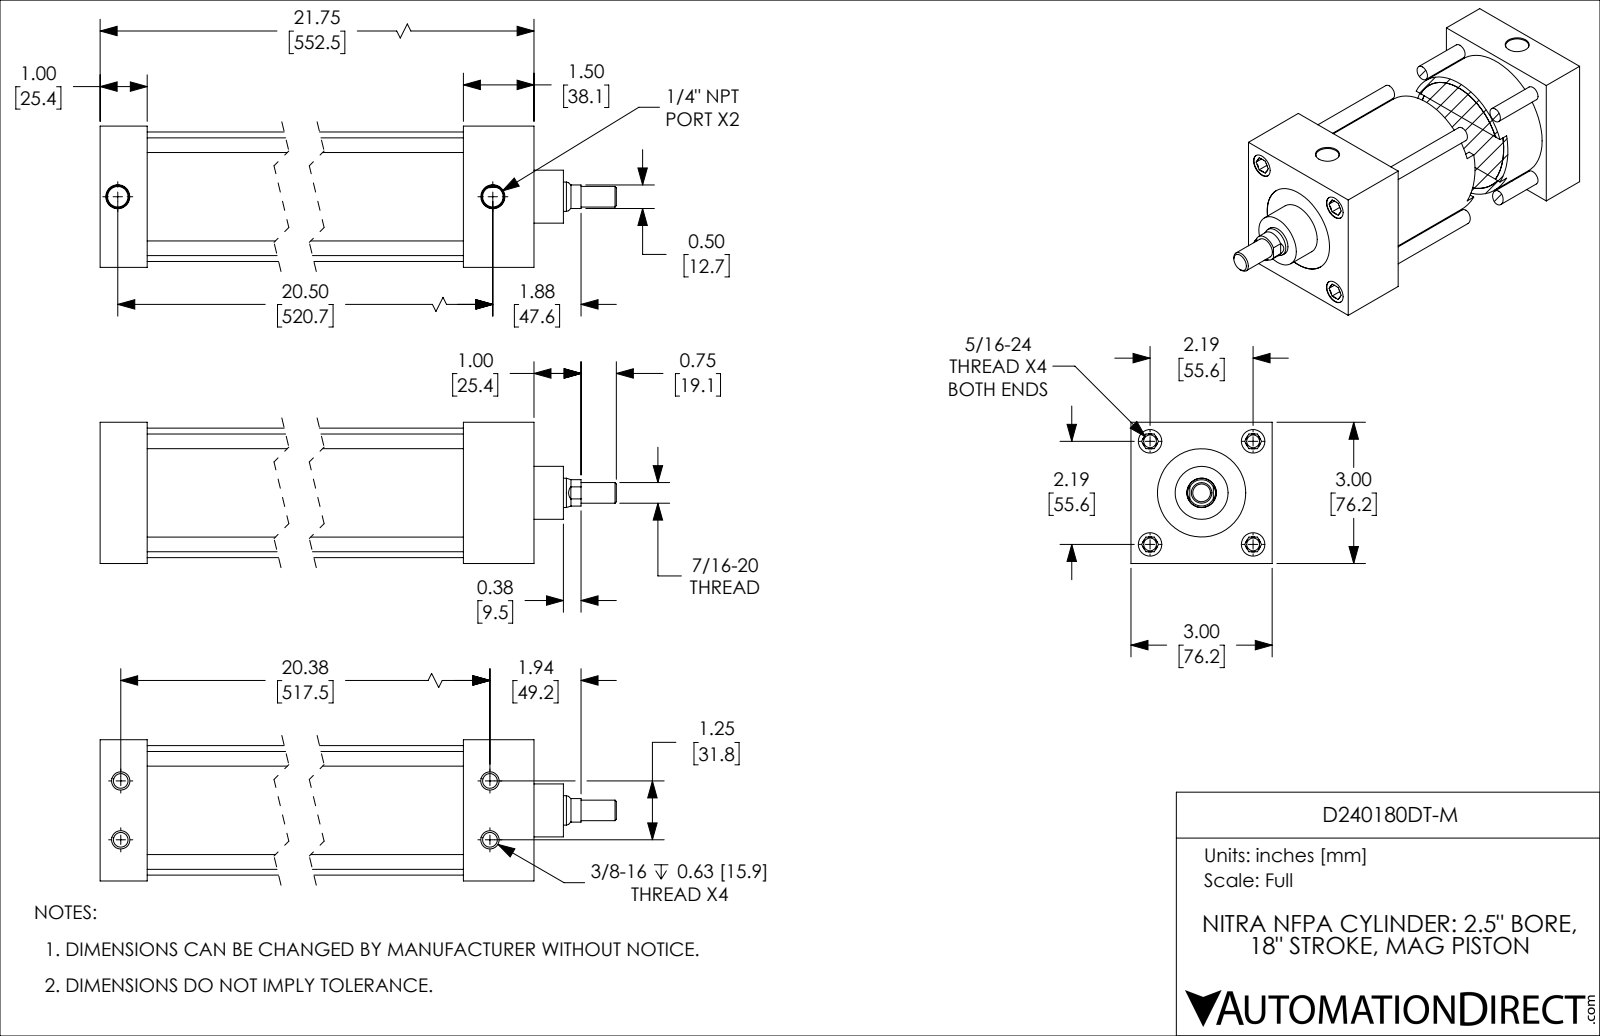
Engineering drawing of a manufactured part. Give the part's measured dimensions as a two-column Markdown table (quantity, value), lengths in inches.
| quantity | value |
| --- | --- |
| part name | D240180DT-M_PISTON_KK1; D240180DT-M; D240180DT-M_BODY |
| STEP written by | SolidWorks 2019 (CONFIG_CONTROL_DESIGN) |
| units | inches |
| bodies | 2 solids, 200 faces (58 planar, 62 cylindrical, 80 other) |
| overall size | 23.5 × 3 × 3 |
| volume | 59.61 in³ |
| surface area | 535 in² |
| round holes (diameter × count) | 0.272 × 4, 0.313 × 4, 0.5 × 4, 0.438 × 2, 0.626 × 1, 1.875 × 1, 2.501 × 1 |
| round bosses / shafts (diameter × count) | 0.312 × 4, 2.751 × 1, 2.499 × 1, 1.125 × 1, 0.624 × 1, 0.437 × 1 |
| partial cylindrical surfaces (radius × count) | 0.281 × 1 |
| main face-to-face distances | 3, 1, 20.25, 19.25, 21.75, 20.75, 1.5, 1.25, 2.25, 18 |
| hole center spacings | 1.548, 2.19, 0.628, 0.628, 1.25, 3.097, 20.375, 20.413 |
